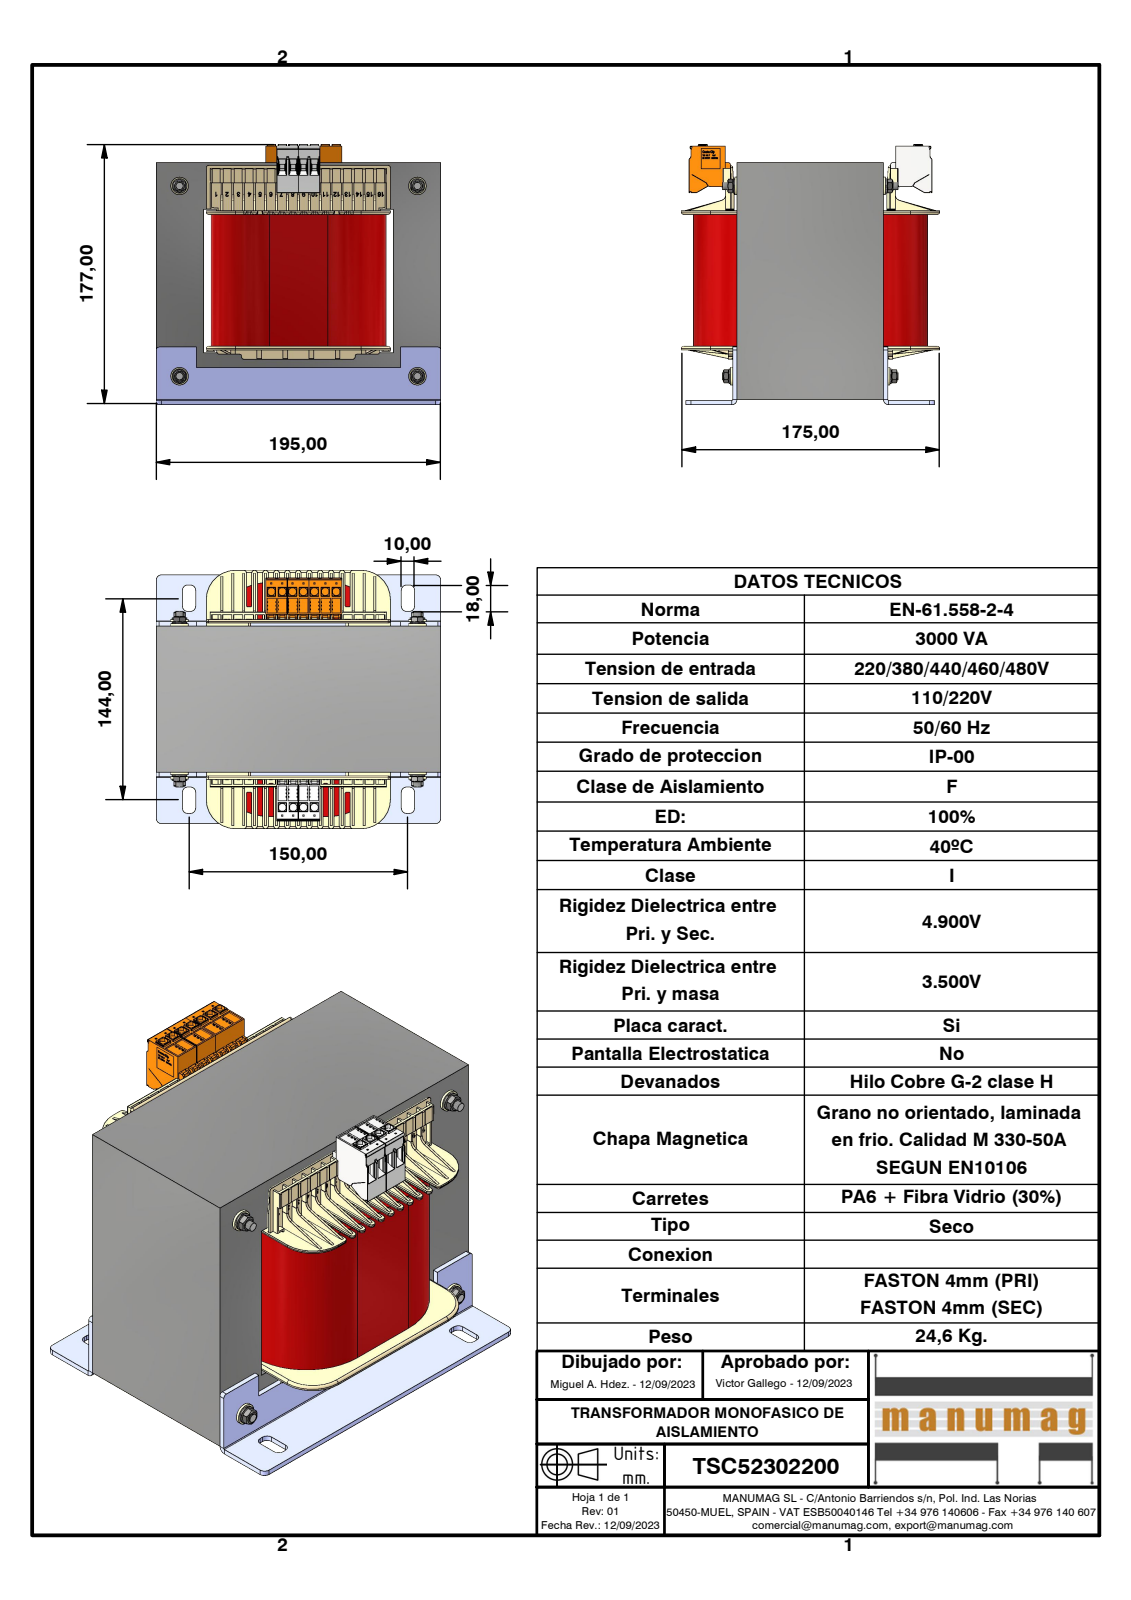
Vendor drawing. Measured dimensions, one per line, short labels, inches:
name: TSC52302200; EI195 x 162 - 100 (Rc65); EI192_104_AK_25373_2_Wz837 BOBINADO; EI192_104_AK_25373_2_Wz837 (+8 more)
written by: Autodesk Inventor 2023 (AUTOMOTIVE_DESIGN)
unit: in
bodies: 38 solids, 11220 faces (8342 planar, 1301 cylindrical, 1577 other)
size: 7.677 × 7.008 × 6.953
volume: 226.1 in³; area: 840 in²
holes: 4× ⌀0.163, 4× ⌀0.197, 4× ⌀0.209, 4× ⌀0.433, 2× ⌀0.39
bosses: 4× ⌀0.472, 4× ⌀0.394, 4× ⌀0.232
rounds: 425× R0.006, 132× R0.008, 52× R0.039, 44× R0.059, 42× R0.02, 22× R0.077, 22× R0.138, 12× R0.012
face distances: 1.28, 5.118, 0.118, 6.398, 0.094, 3.937, 2.559, 3.646, 0.079, 3.839
hole spacings: 5.118, 6.417, 8.208
